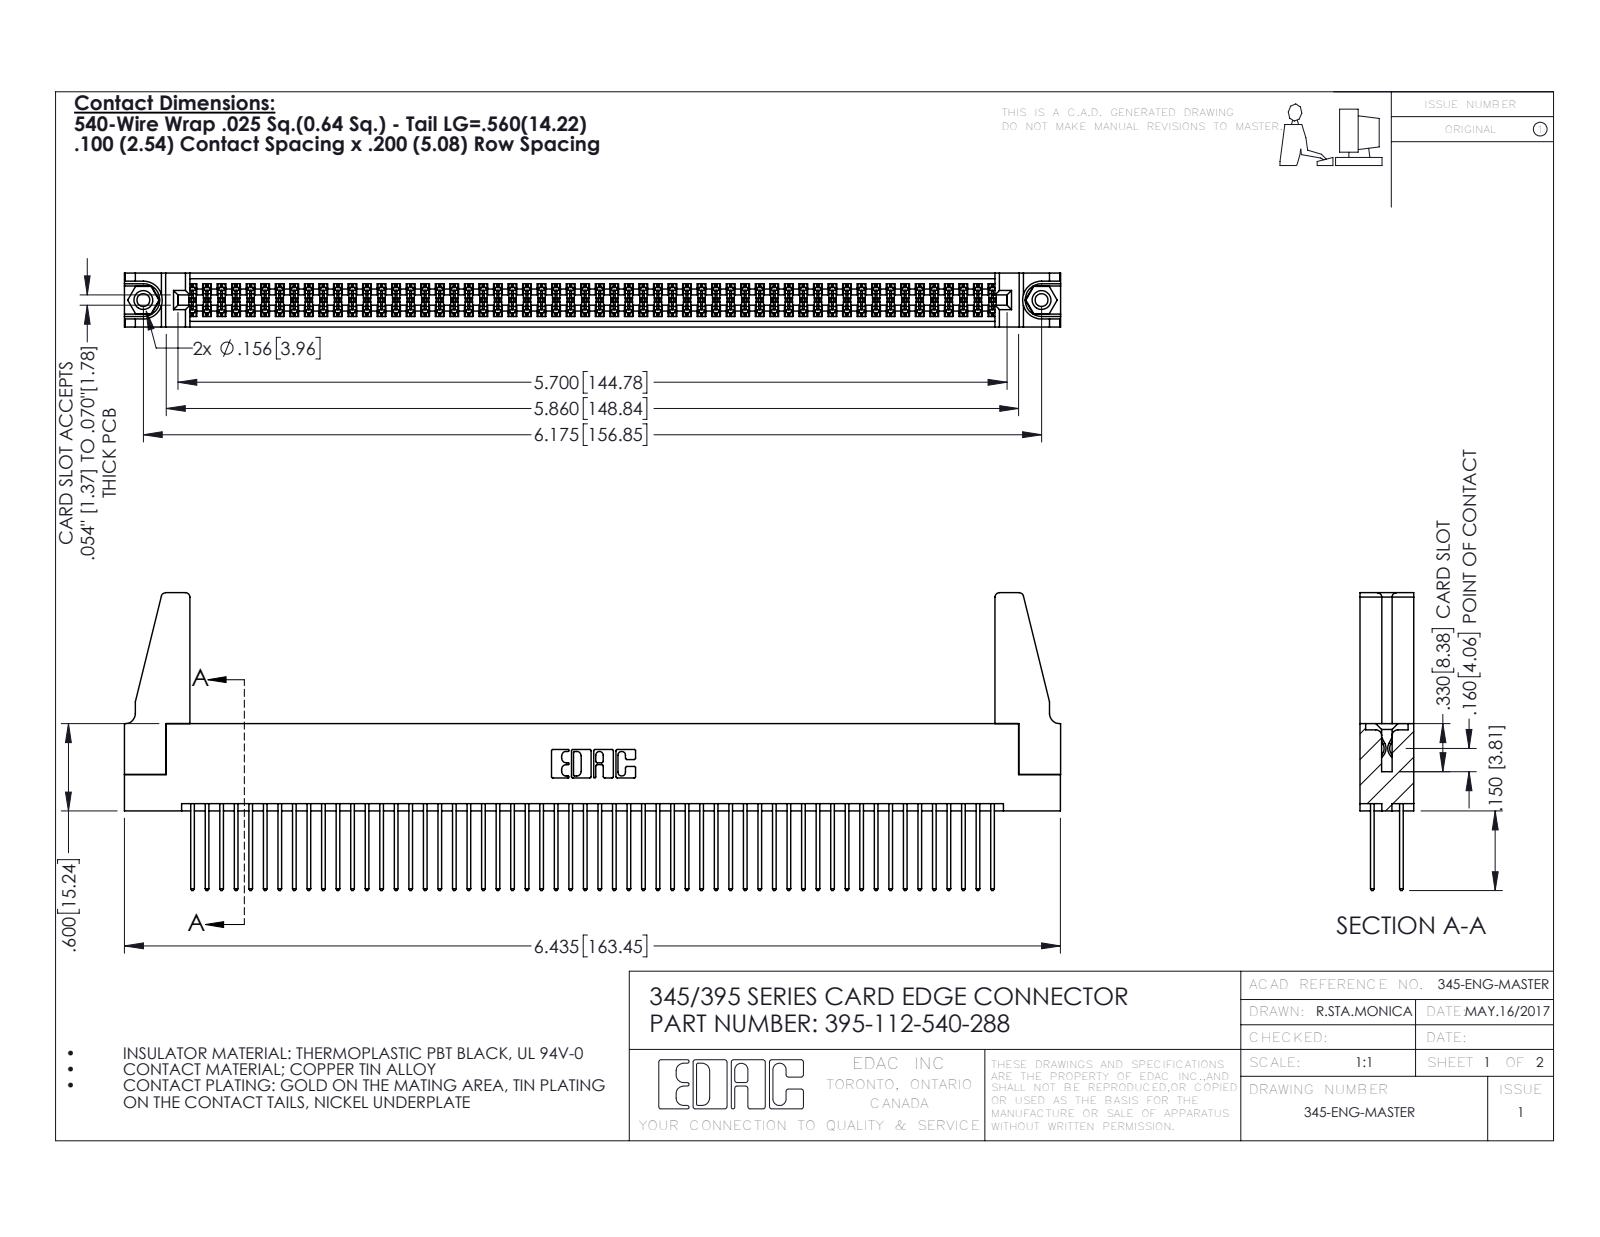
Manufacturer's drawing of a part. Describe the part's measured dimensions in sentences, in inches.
The part is named "345-250-001_345-250-001-102; 345-220-078_345-220-088; 345 Part_Flush Mounting Lugs - 0.156 Dia-TH; 395-112-540-288 (+1 more)". Its 3-D file was written by "SolidWorks 2016 (CONFIG_CONTROL_DESIGN)". It is 117 solids with 5850 faces: 3848 planar, 1986 cylindrical and 16 other. Overall it measures 6.436 by 2.047 by 0.37 inches. Its volume is 1.201 cubic inches and its surface area 45.97 square inches. Round holes: 2 of diameter 0.089, 2 of diameter 0.125, 2 of diameter 0.156, 1 of diameter 0.064. Round bosses or shafts: 2 of diameter 0.155. Partial cylindrical surfaces (rounded edges, fillets, slot ends): 168 of radius 0.006, 112 of radius 0.01, 22 of radius 0.01, 8 of radius 0.03, 6 of radius 0.007, 6 of radius 0.031, 3 of radius 0.026, 2 of radius 0.014. The main face-to-face distances are 0.072, 0.298, 0.2, 0.098, 0.272, 0.025, 0.37, 0.225, 0.175, 0.149. The hole center spacings are 0.27, 5.939, 6.175.
